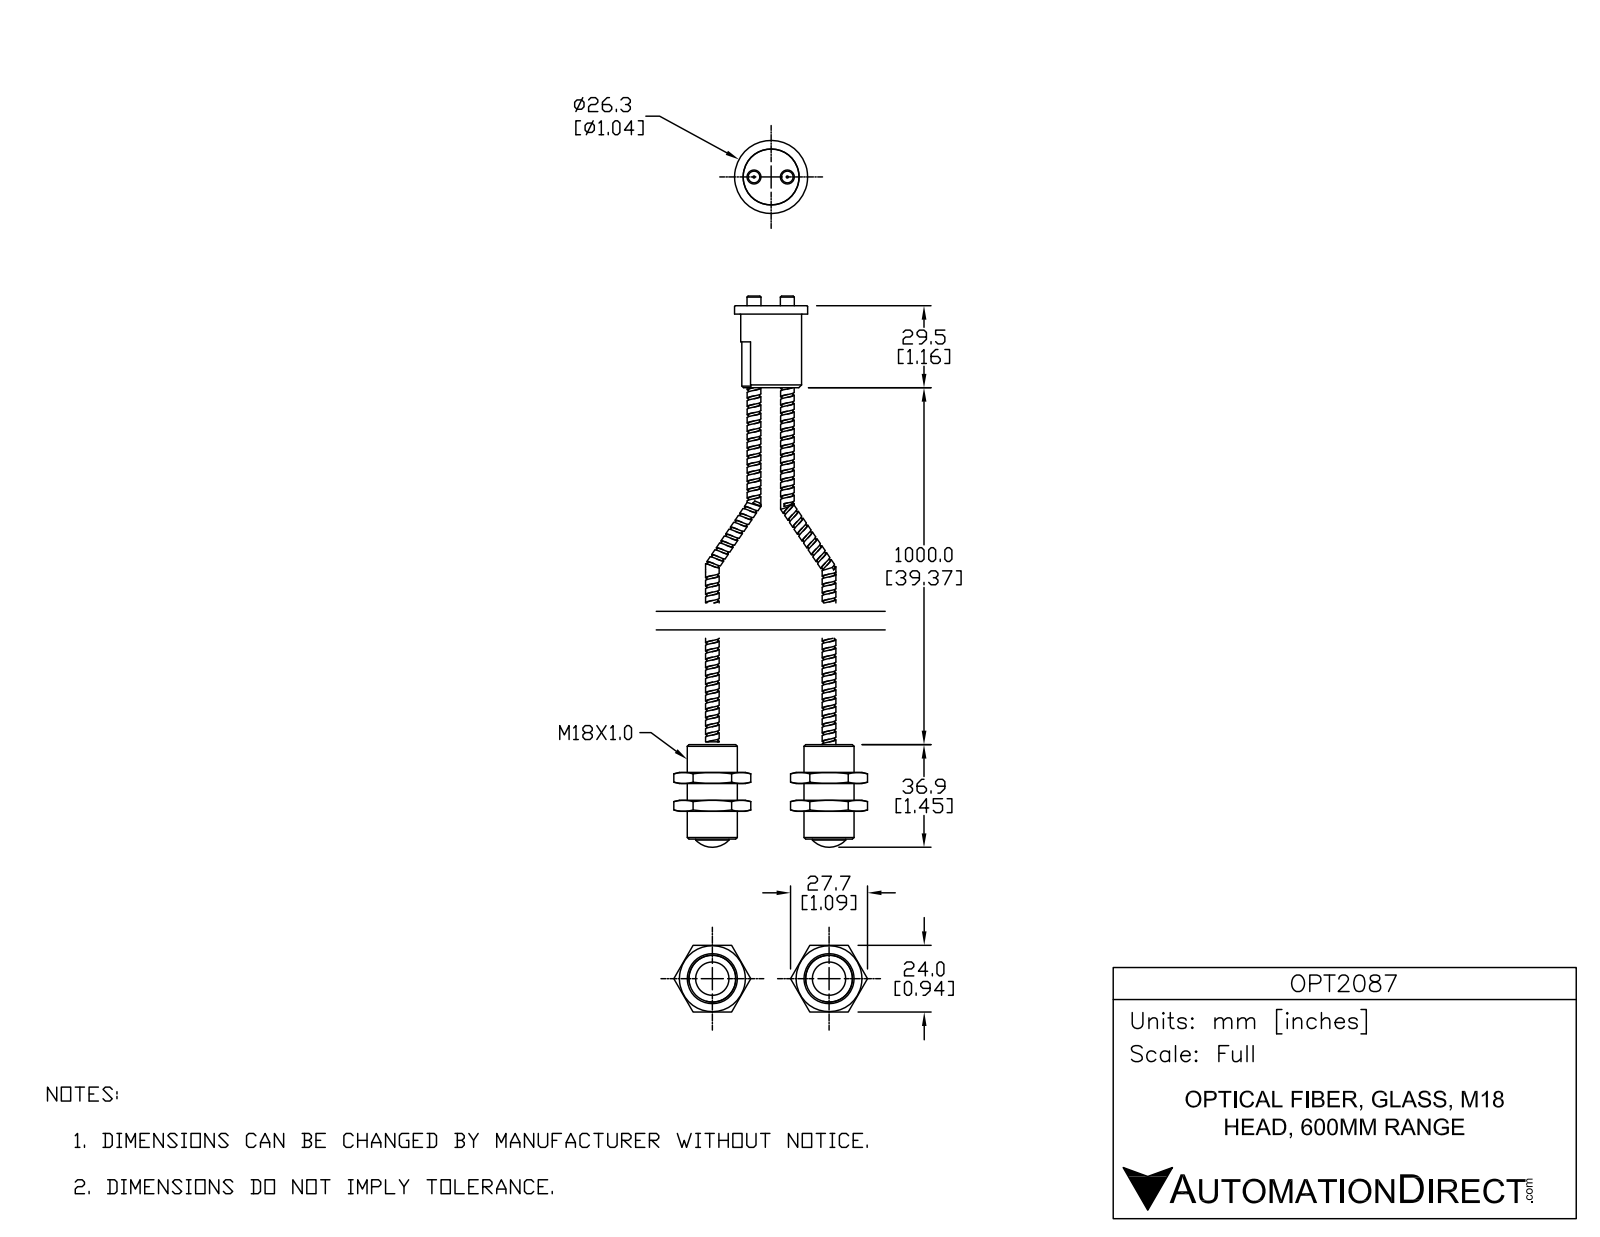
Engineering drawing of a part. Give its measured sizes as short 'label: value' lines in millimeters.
name: 1011977_SCHLAUCH_MS__4-9_SLK2320
written by: Unknown (AUTOMOTIVE_DESIGN)
unit: mm
bodies: 2 solids, 415 faces (56 planar, 316 cylindrical, 43 other)
size: 531.91 × 69.71 × 26.3
volume: 46 362 mm³; area: 28 013 mm²
holes: 2× ⌀0.75, 1× ⌀20.15
bosses: 6× ⌀4.9, 2× ⌀18, 2× ⌀12, 2× ⌀5, 1× ⌀26.3, 1× ⌀21.9, 1× ⌀20.1, 1× ⌀19.9
rounds: 1× R10.55
face distances: 10, 24, 14, 4, 20, 491.5, 36.37, 501.5, 515.5, 511.5
hole spacings: 5.85, 6.15, 12
